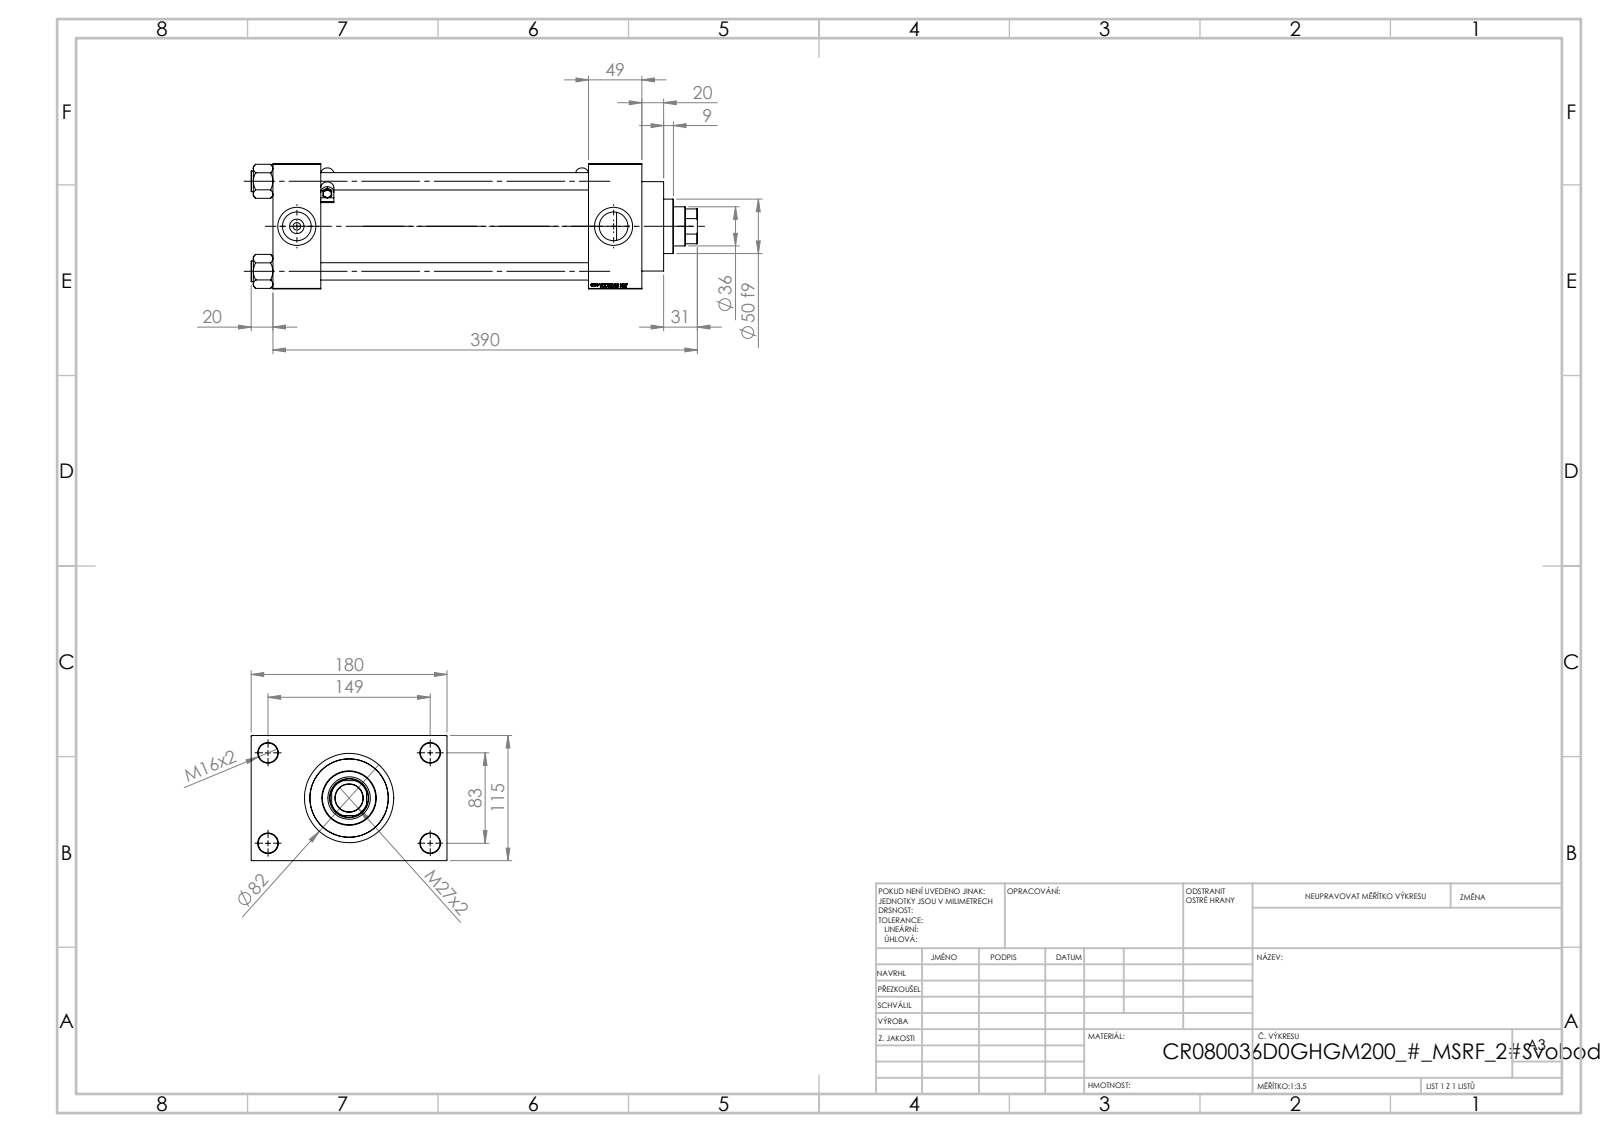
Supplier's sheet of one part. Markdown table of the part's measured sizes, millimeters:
| quantity | value |
| --- | --- |
| part name | V215CR_D_Body; V215_VC_A; V215CR_VCP_D; MSRF_MSRG1 (+2 more) |
| STEP written by | SolidWorks 2019 (CONFIG_CONTROL_DESIGN) |
| units | millimeters |
| bodies | 13 solids, 1215 faces (581 planar, 116 cylindrical, 518 other) |
| overall size | 410 × 180 × 115 |
| volume | 2 456 000 mm³ |
| surface area | 451 723 mm² |
| round holes (diameter × count) | 16 × 4, 18 × 4, 7 × 2, 26.44 × 2, 35 × 2, 25.5 × 1, 36 × 1, 39 × 1, 61 × 1, 72 × 1, 80 × 1 |
| round bosses / shafts (diameter × count) | 19 × 4, 5 × 2, 2.5 × 2, 86 × 1, 82 × 1, 50 × 1 |
| partial cylindrical surfaces (radius × count) | 0.5 × 12, 6 × 4, 17.5 × 1 |
| main face-to-face distances | 115, 246, 295, 49, 44, 290, 339, 32.5, 147.5, 180 |
| hole center spacings | 33.15, 58.48, 82.7, 85.28, 89.24, 115.85, 142.43, 83 |
